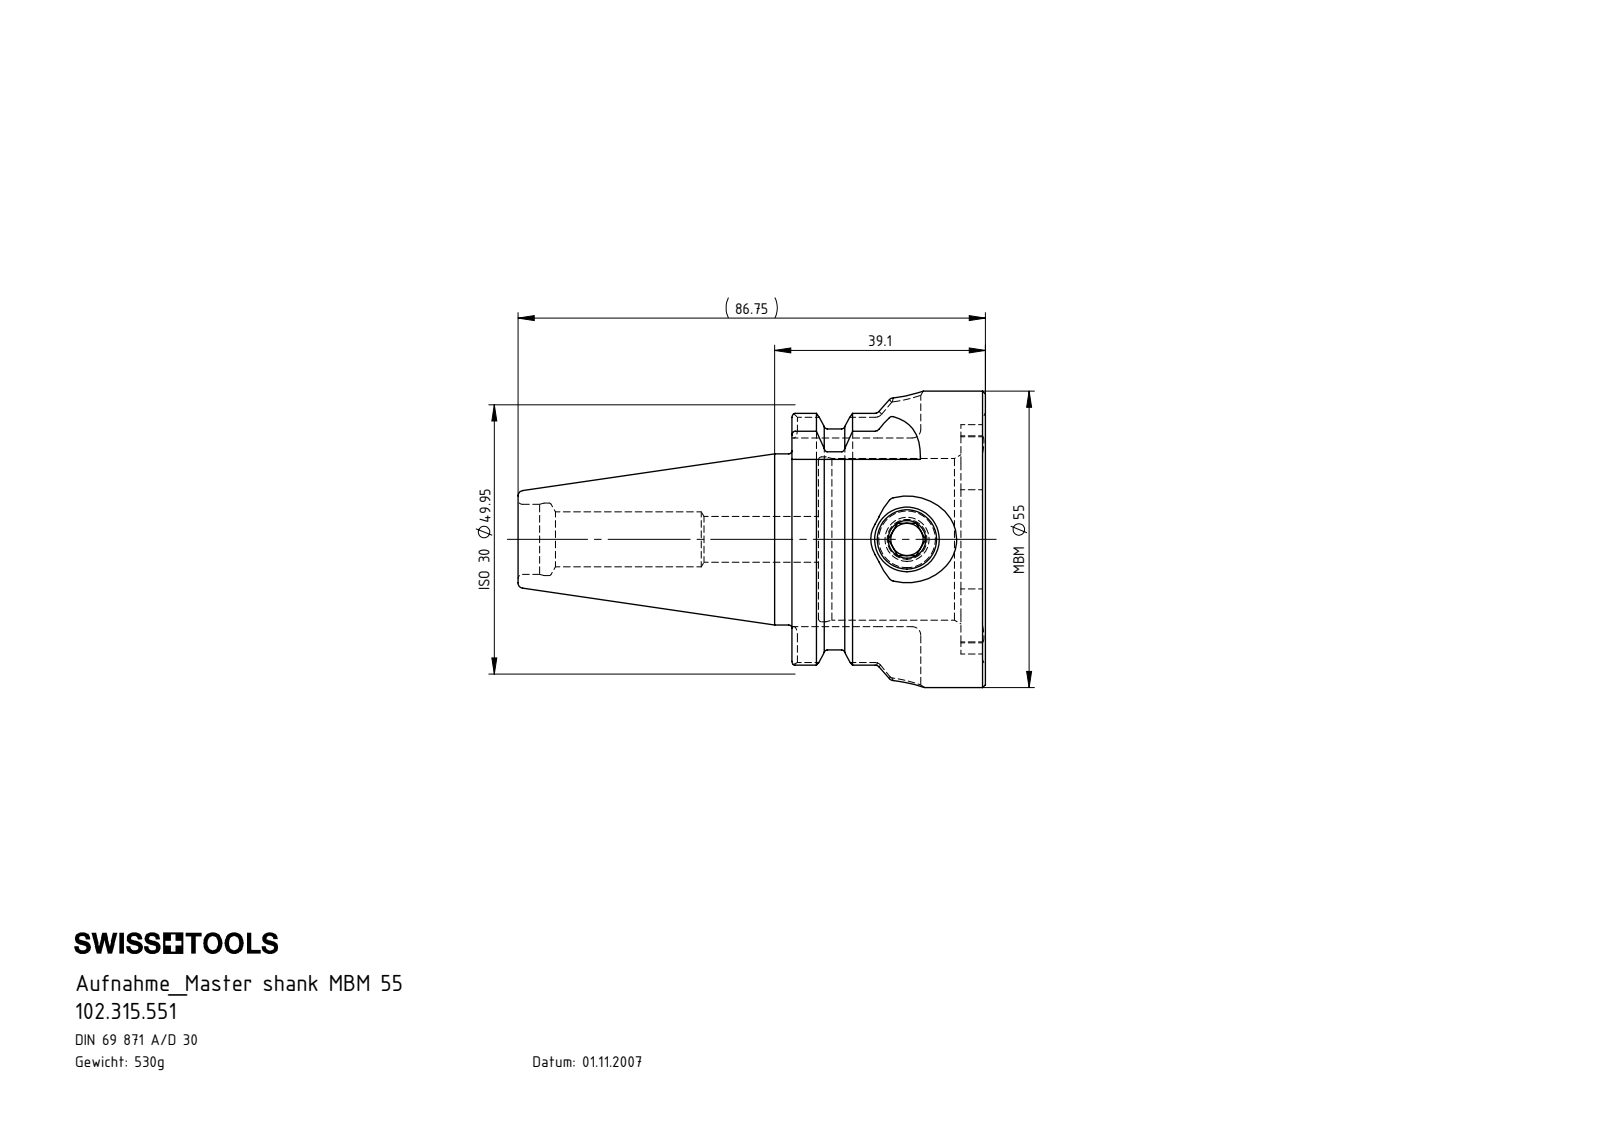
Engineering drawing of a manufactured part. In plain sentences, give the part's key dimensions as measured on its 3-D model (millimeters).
The part is named "MB5-ER1.001.017_A; SK3-MB5.K01.039_C; 102.315.551". Its 3-D file was written by "SolidWorks 2017 (CONFIG_CONTROL_DESIGN)". It is 2 solids with 195 faces: 49 planar, 54 cylindrical and 92 other. Overall it measures 86.75 by 55 by 55 millimeters. Its volume is 67 486 cubic millimeters and its surface area 20 207 square millimeters. Round holes: 1 of diameter 6, 1 of diameter 8.5, 1 of diameter 10.2, 1 of diameter 11, 1 of diameter 13, 1 of diameter 13.45, 1 of diameter 30, 1 of diameter 30.6. Round bosses or shafts: 1 of diameter 55, 1 of diameter 31.75, 1 of diameter 12. Partial cylindrical surfaces (rounded edges, fillets, slot ends): 8 of radius 1.6, 4 of radius 5.2, 1 of radius 8, 1 of radius 8.05, 1 of radius 18.5, 1 of radius 21.27, 1 of radius 22.02, 1 of radius 24.98. The main face-to-face distances are 4.9, 35.9, 31, 31.35, 26.45, 4.55, 35, 35.35, 30.45, 4.
